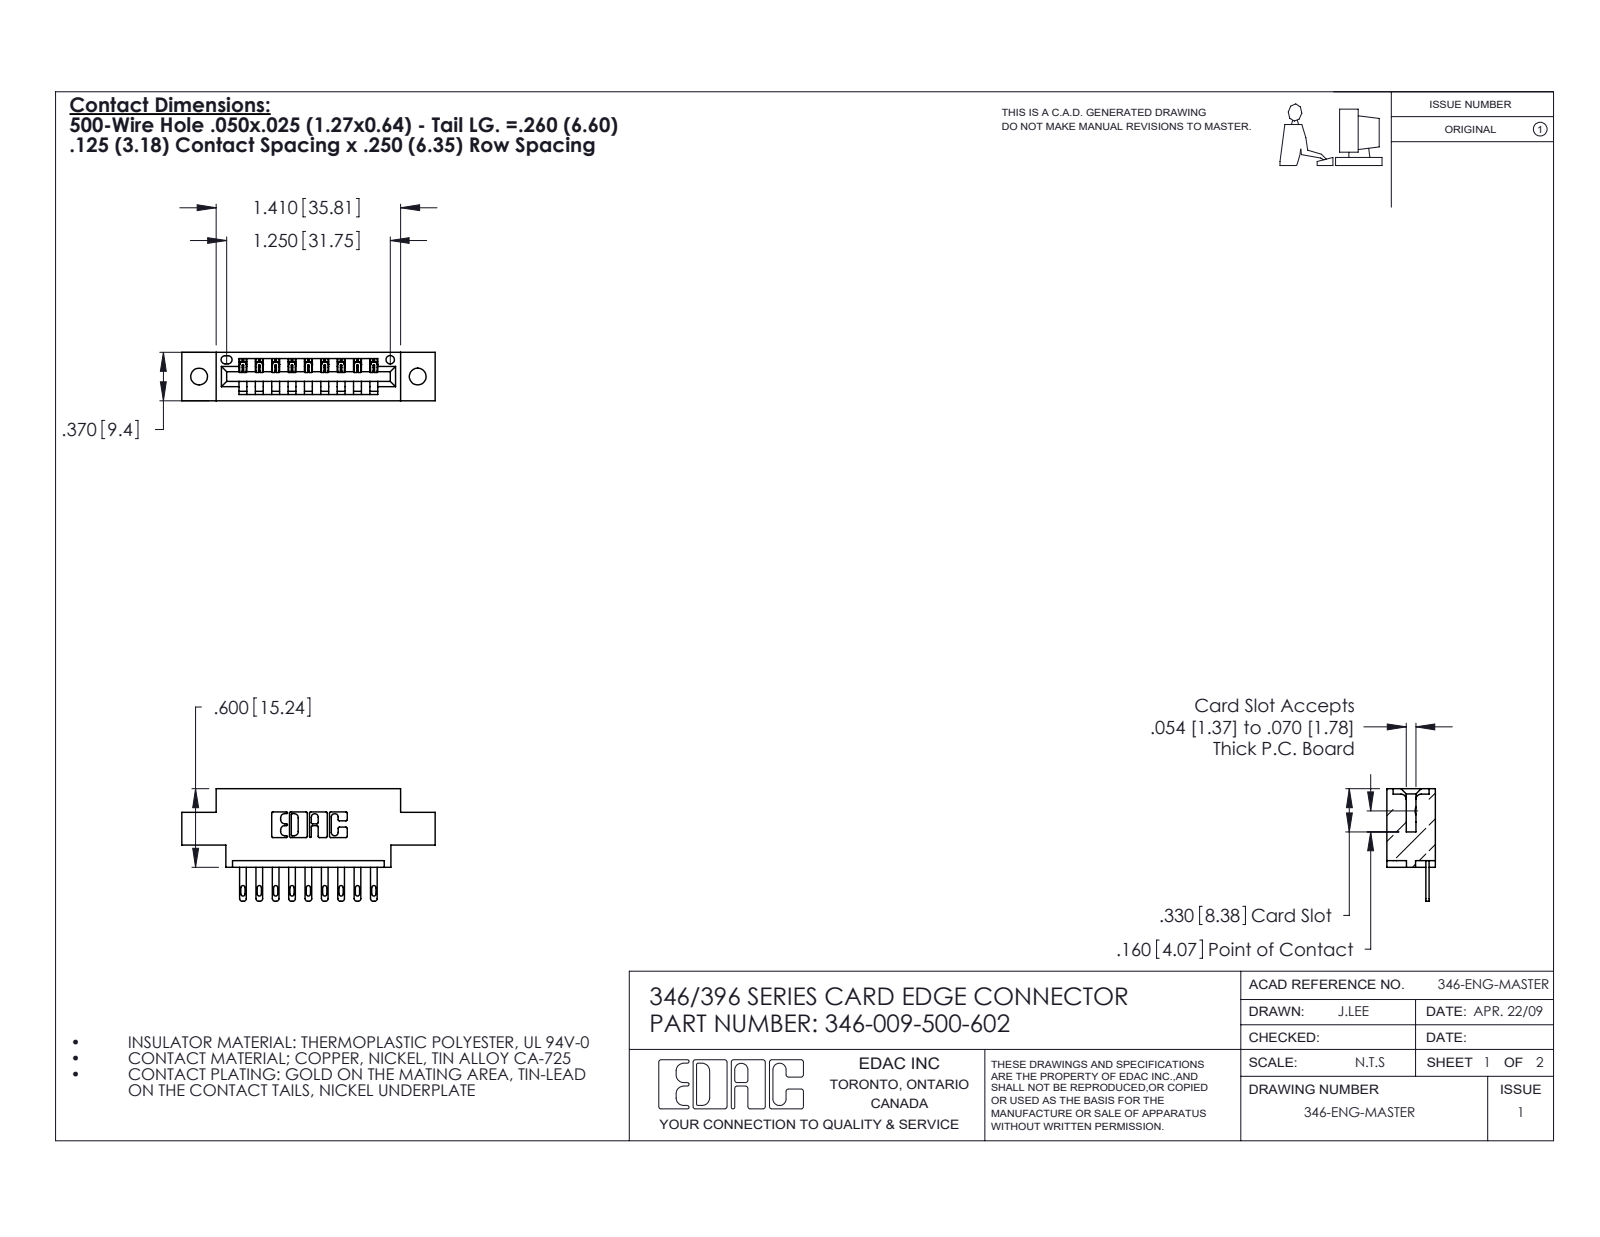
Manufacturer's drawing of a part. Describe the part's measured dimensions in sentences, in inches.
The part is named "346-009-500-602; 346 Part_0.170 Offset - 0.128 Dia; 345-292-001_345-293-100". Its 3-D file was written by "SolidWorks 2020 (CONFIG_CONTROL_DESIGN)". It is 10 solids with 612 faces: 386 planar, 226 cylindrical and 0 other. Overall it measures 1.935 by 0.86 by 0.37 inches. Its volume is 0.262 cubic inches and its surface area 7.623 square inches. Round holes: 2 of diameter 0.128, 1 of diameter 0.064. Partial cylindrical surfaces (rounded edges, fillets, slot ends): 22 of radius 0.01, 18 of radius 0.006, 18 of radius 0.016, 18 of radius 0.02, 6 of radius 0.007, 6 of radius 0.031, 3 of radius 0.026, 2 of radius 0.031. The main face-to-face distances are 0.25, 0.37, 0.048, 0.322, 0.072, 0.298, 0.025, 0.148, 0.222, 0.1. The hole center spacings are 0.246, 1.465, 1.67.
